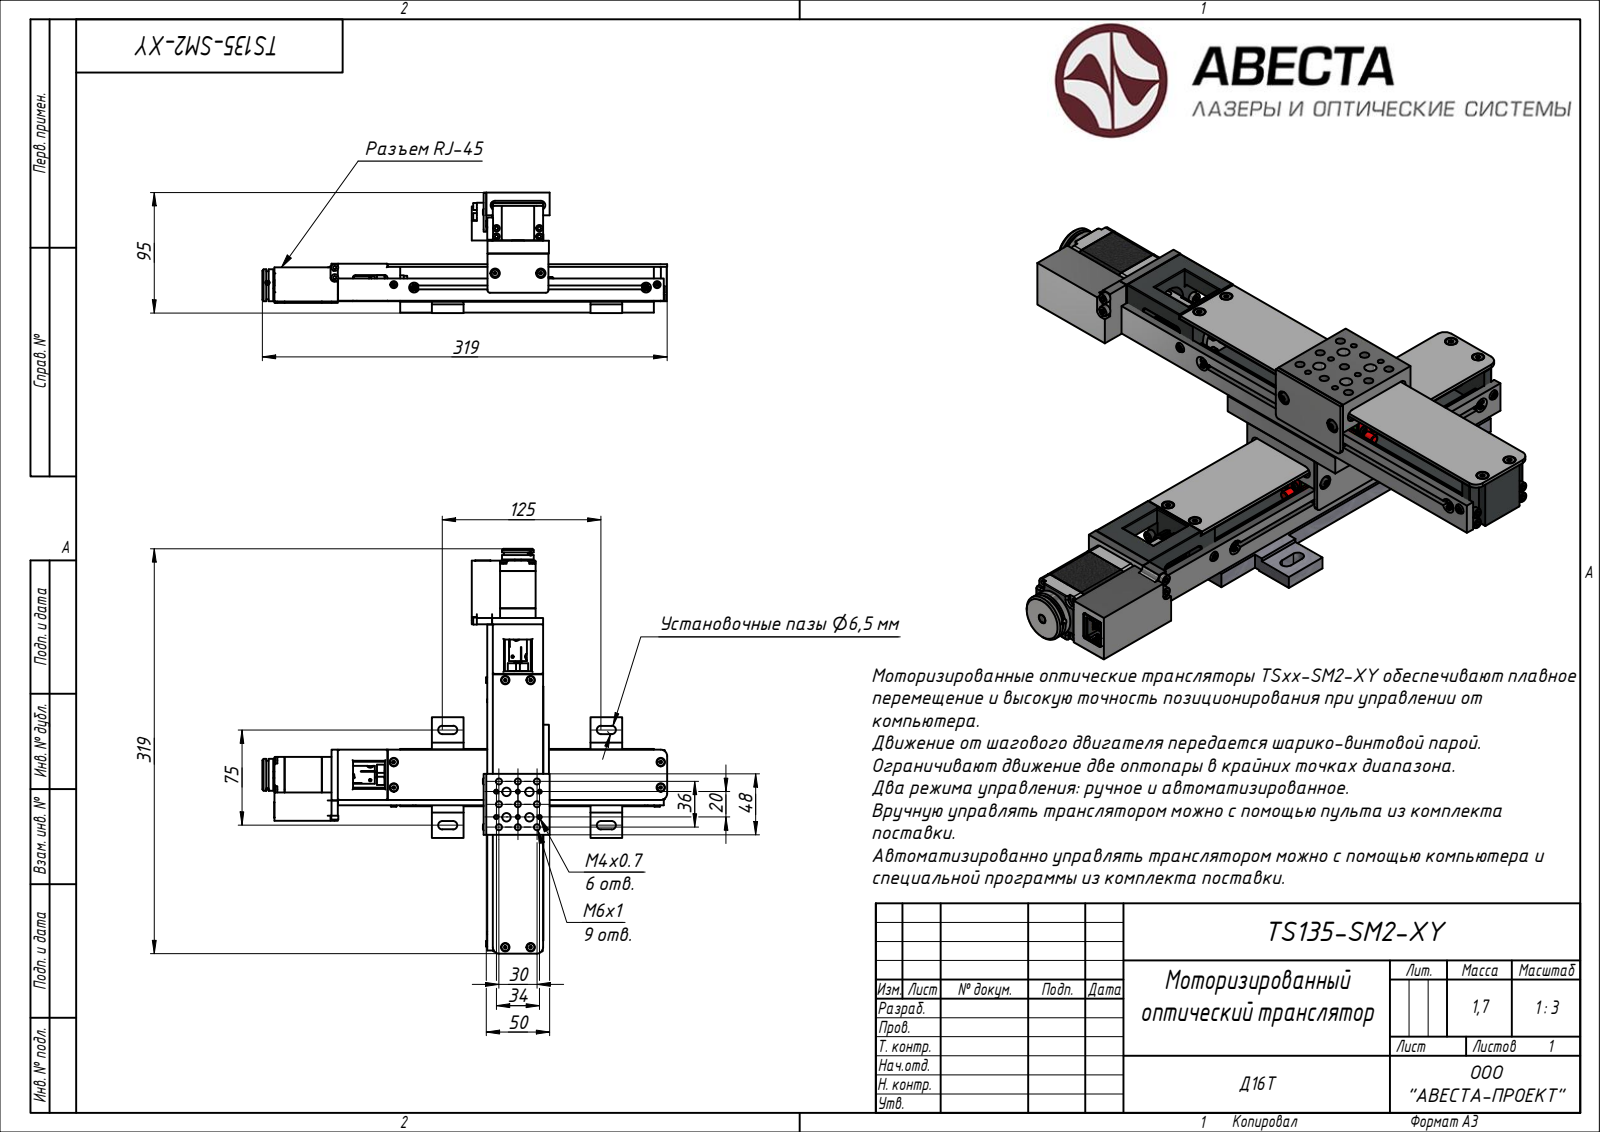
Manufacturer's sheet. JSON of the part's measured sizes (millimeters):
{"part_name": "Block 01", "step_written_by": "ST-DEVELOPER v15 (AUTOMOTIVE_DESIGN)", "units": "millimeters", "bodies": {"solids": 88, "faces": 5028, "planar": 0, "cylindrical": 0, "other": 5028}, "overall_size": [318.8, 318.8, 95]}
